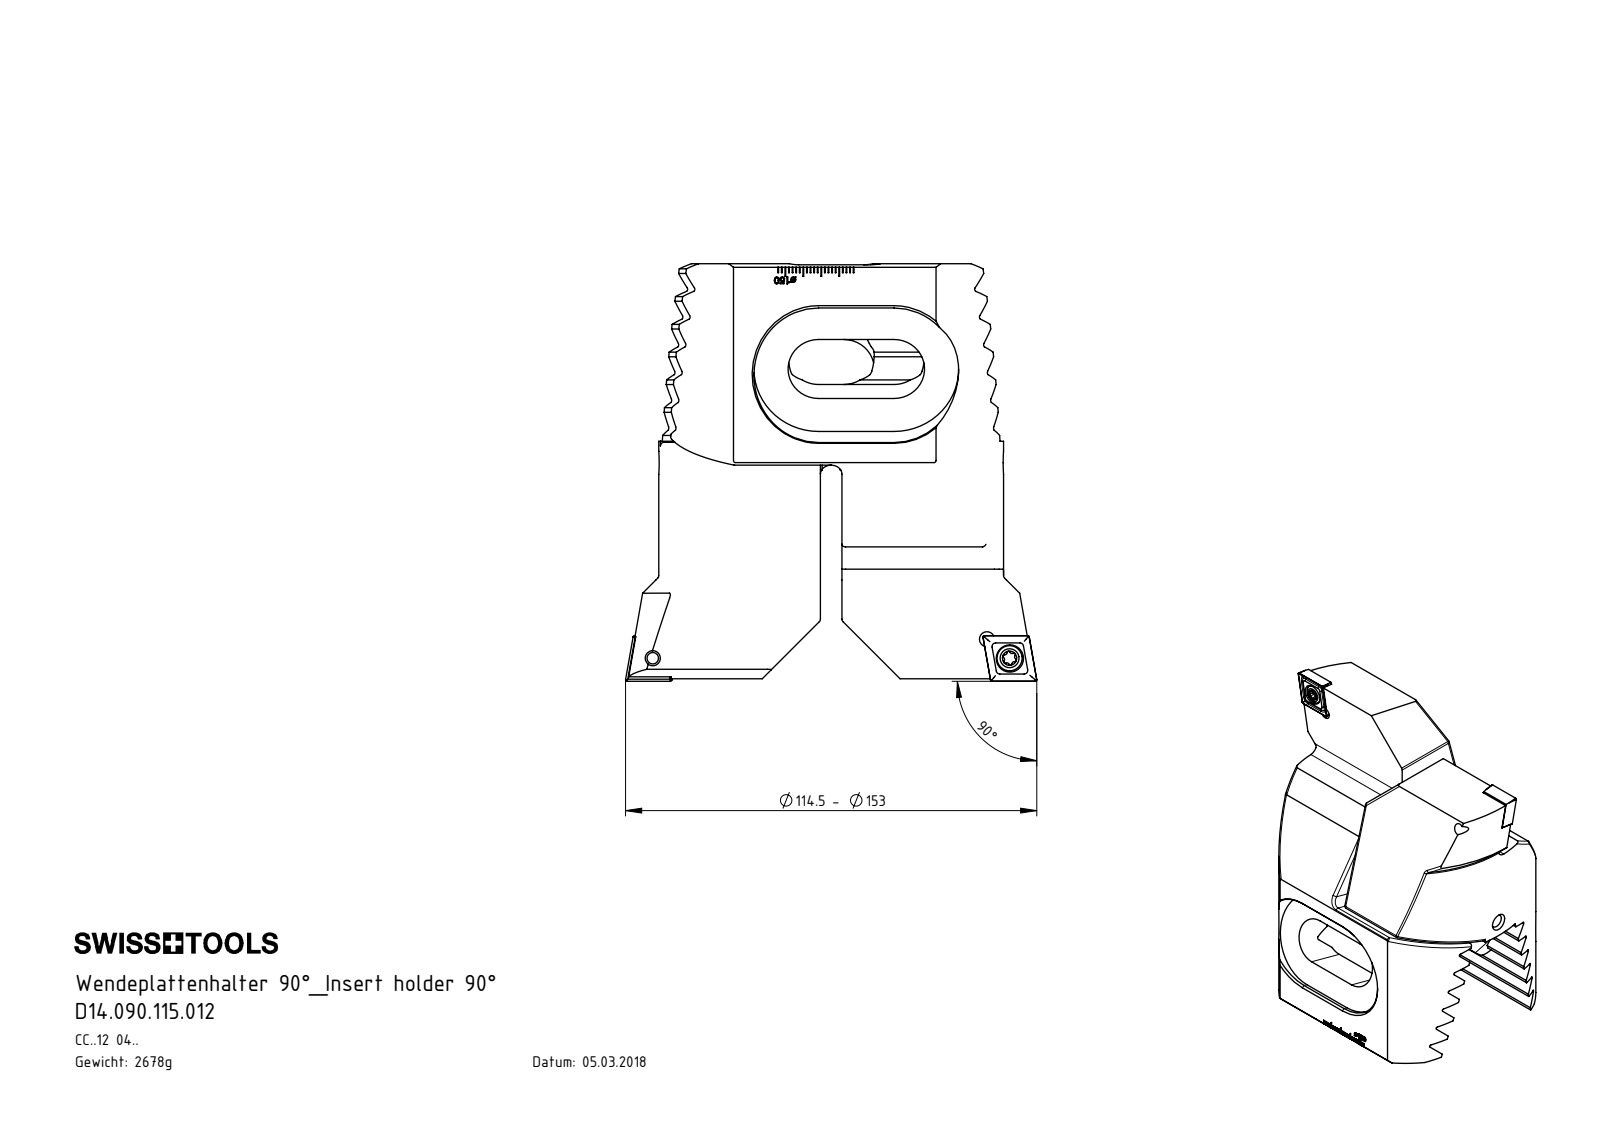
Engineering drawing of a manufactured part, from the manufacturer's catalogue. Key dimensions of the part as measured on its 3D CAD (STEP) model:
Part name (STEP PRODUCT): WCC-ER2.001.010_A; Z94-ER3.001.040; CCMT120404; D14.090.115.012 (+1 more)
STEP written by: SolidWorks 2015 (AUTOMOTIVE_DESIGN)
Units: millimetres
Bodies: 8 solids, 414 faces (164 planar, 136 cylindrical, 114 other)
Overall size (bounding box): 115.15 × 114.5 × 75
Volume: 339 073 mm³ · Surface area: 64 150 mm²
Round holes (diameter × count): ⌀4.2 ×4, ⌀1 ×2, ⌀5.5 ×2, ⌀7.6 ×2, ⌀5 ×1
Round bosses / shafts (diameter × count): ⌀7 ×2, ⌀5 ×2, ⌀6 ×1, ⌀4 ×1
Partial cylindrical surfaces — rounded edges, fillets, slot ends (radius × count): R0.34 ×12, R0.39 ×12, R0.69 ×12, R1 ×8, R3 ×4, R8.5 ×4, R18 ×4, R30 ×2
Main face-to-face distances: 6.93, 27.71, 20.78, 13.86, 13.85, 12.46, 34.64, 37.2, 37.8, 48.35
Hole centre spacings: 8.3, 8.5, 20, 93.01, 93.17, 99.37, 38.64, 86.5
